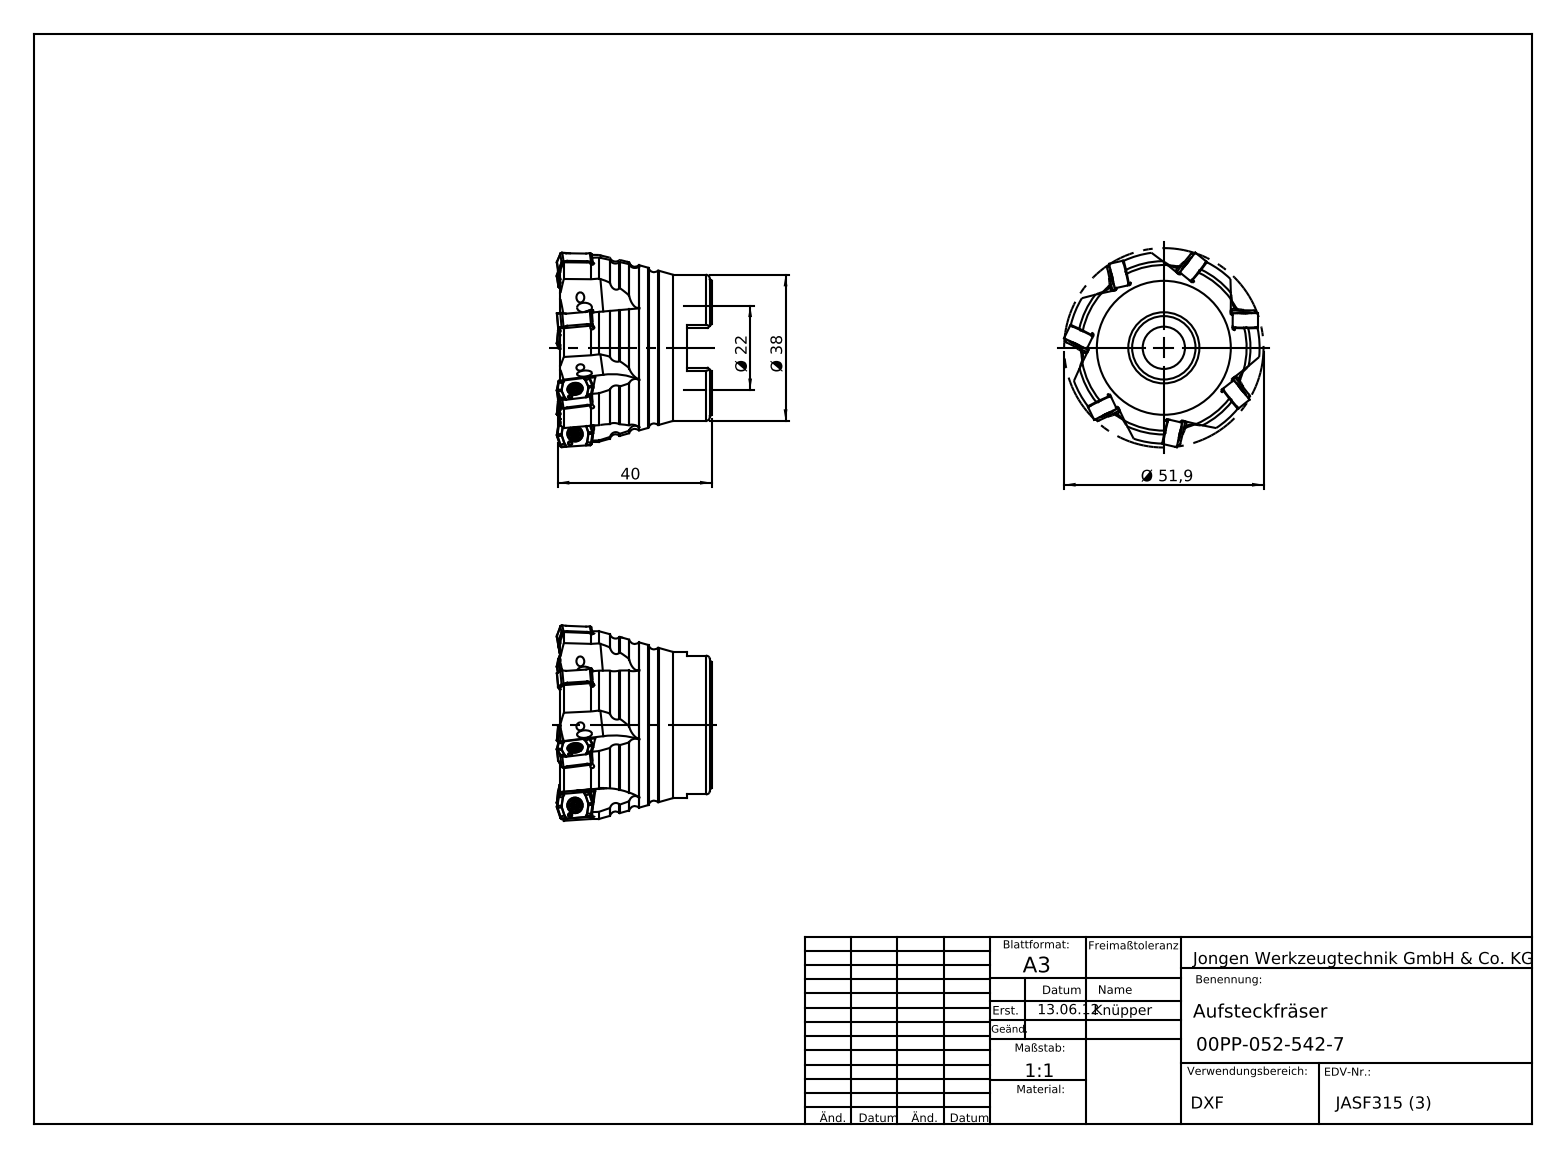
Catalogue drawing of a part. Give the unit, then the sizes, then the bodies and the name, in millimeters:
Units: millimetres
Overall size (bounding box): 48.86 × 48.64 × 38.55
Round holes (diameter × count): ⌀2.5 ×7, ⌀11 ×1, ⌀16.5 ×1, ⌀22 ×1, ⌀22.15 ×1, ⌀22.3 ×1
Round bosses / shafts (diameter × count): ⌀38 ×1
Partial cylindrical surfaces — rounded edges, fillets, slot ends (radius × count): R15 ×7, R24.45 ×1
Main face-to-face distances: 37.8, 6.3, 31.5, 19.95, 13.65, 17.85, 26.8, 20.5, 6.85, 11
Volume: 36 454 mm³ · Surface area: 11 211 mm²
Bodies: 1 solid, 260 faces (114 planar, 37 cylindrical, 109 other)
Part name (STEP PRODUCT): 00PP-052-542-7
STEP written by: SolidWorks 2013 (AUTOMOTIVE_DESIGN)
